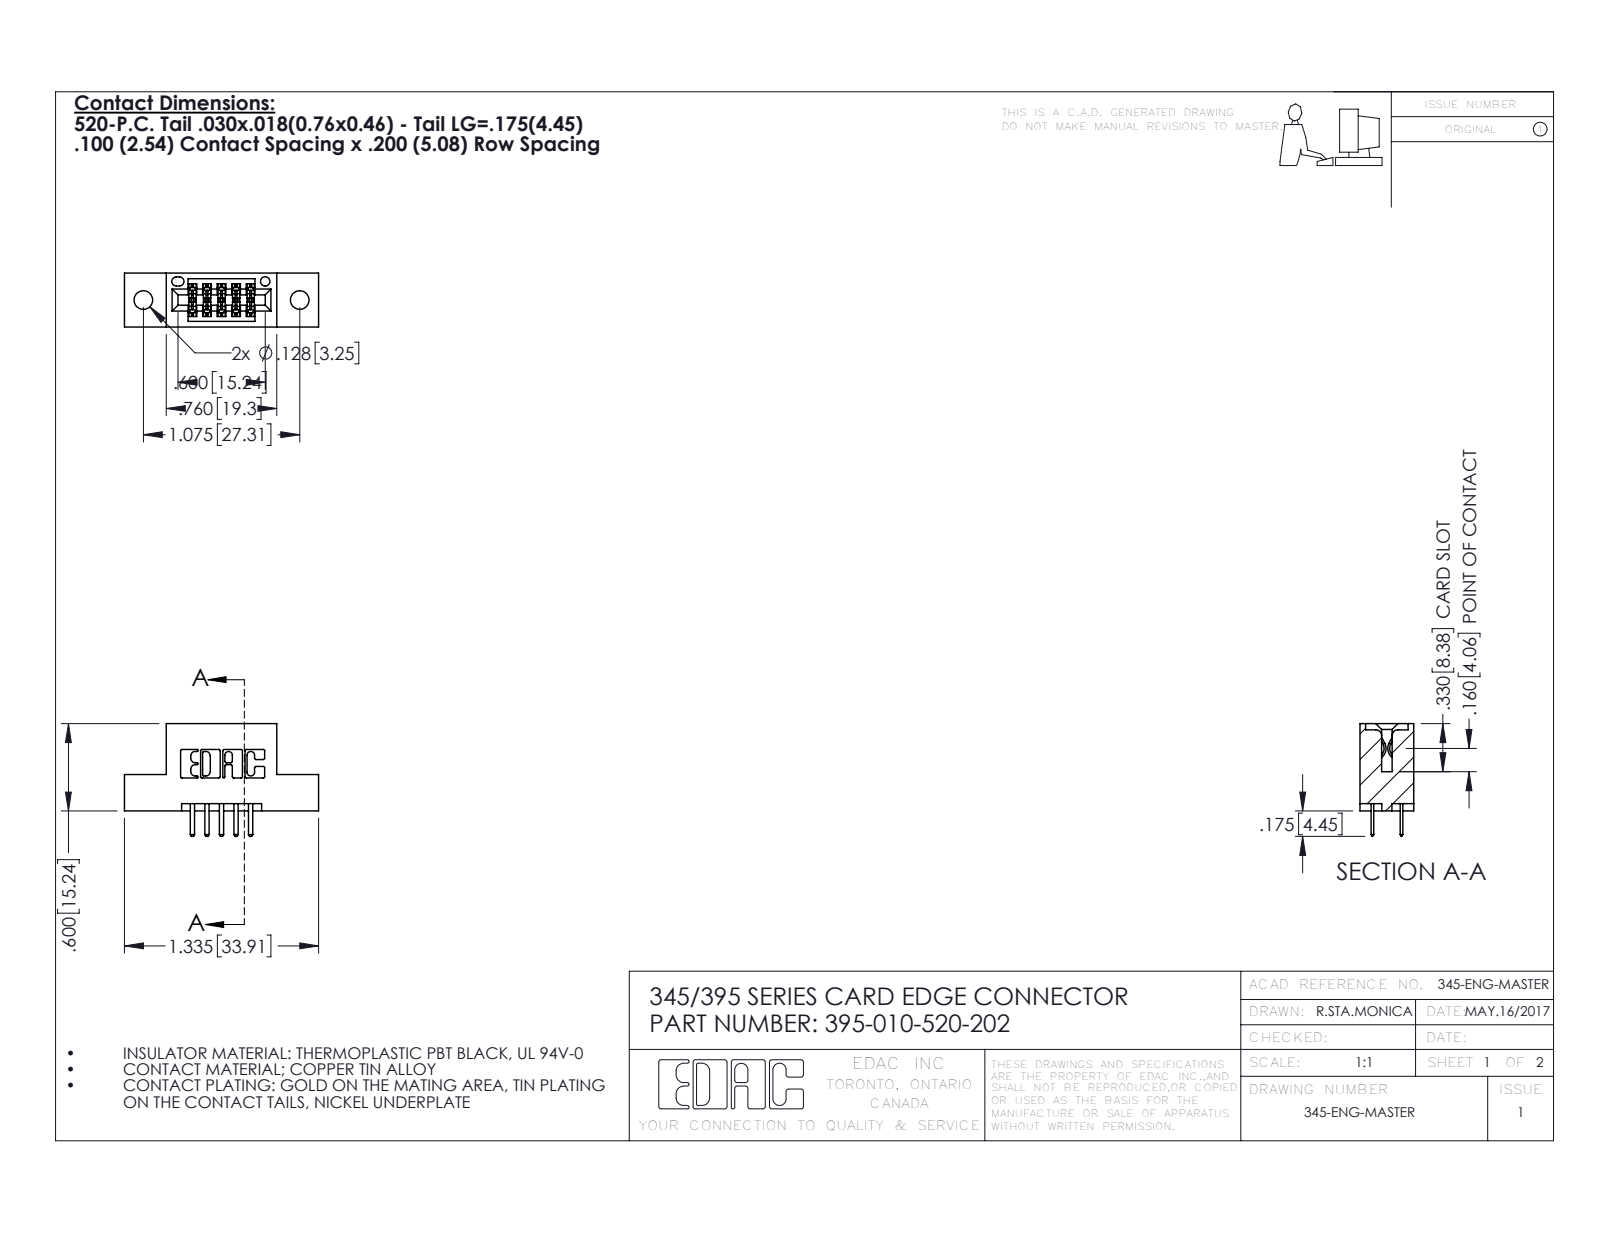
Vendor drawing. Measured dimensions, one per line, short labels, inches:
name: 395-010-520-202; 345 Part_Flush Mounting Lugs - 0.128 Dia; 345-292-001_345-293-120
written by: SolidWorks 2016 (CONFIG_CONTROL_DESIGN)
unit: in
bodies: 11 solids, 666 faces (430 planar, 236 cylindrical, 0 other)
size: 1.335 × 0.775 × 0.37
volume: 0.178 in³; area: 5.118 in²
holes: 2× ⌀0.128, 1× ⌀0.064
rounds: 22× R0.01, 15× R0.006, 14× R0.01, 6× R0.007, 6× R0.031, 3× R0.026, 2× R0.014, 2× R0.019
face distances: 0.2, 0.37, 0.298, 0.072, 0.1, 0.25, 0.098, 0.272, 0.025, 0.06
hole spacings: 0.27, 0.847, 1.075
